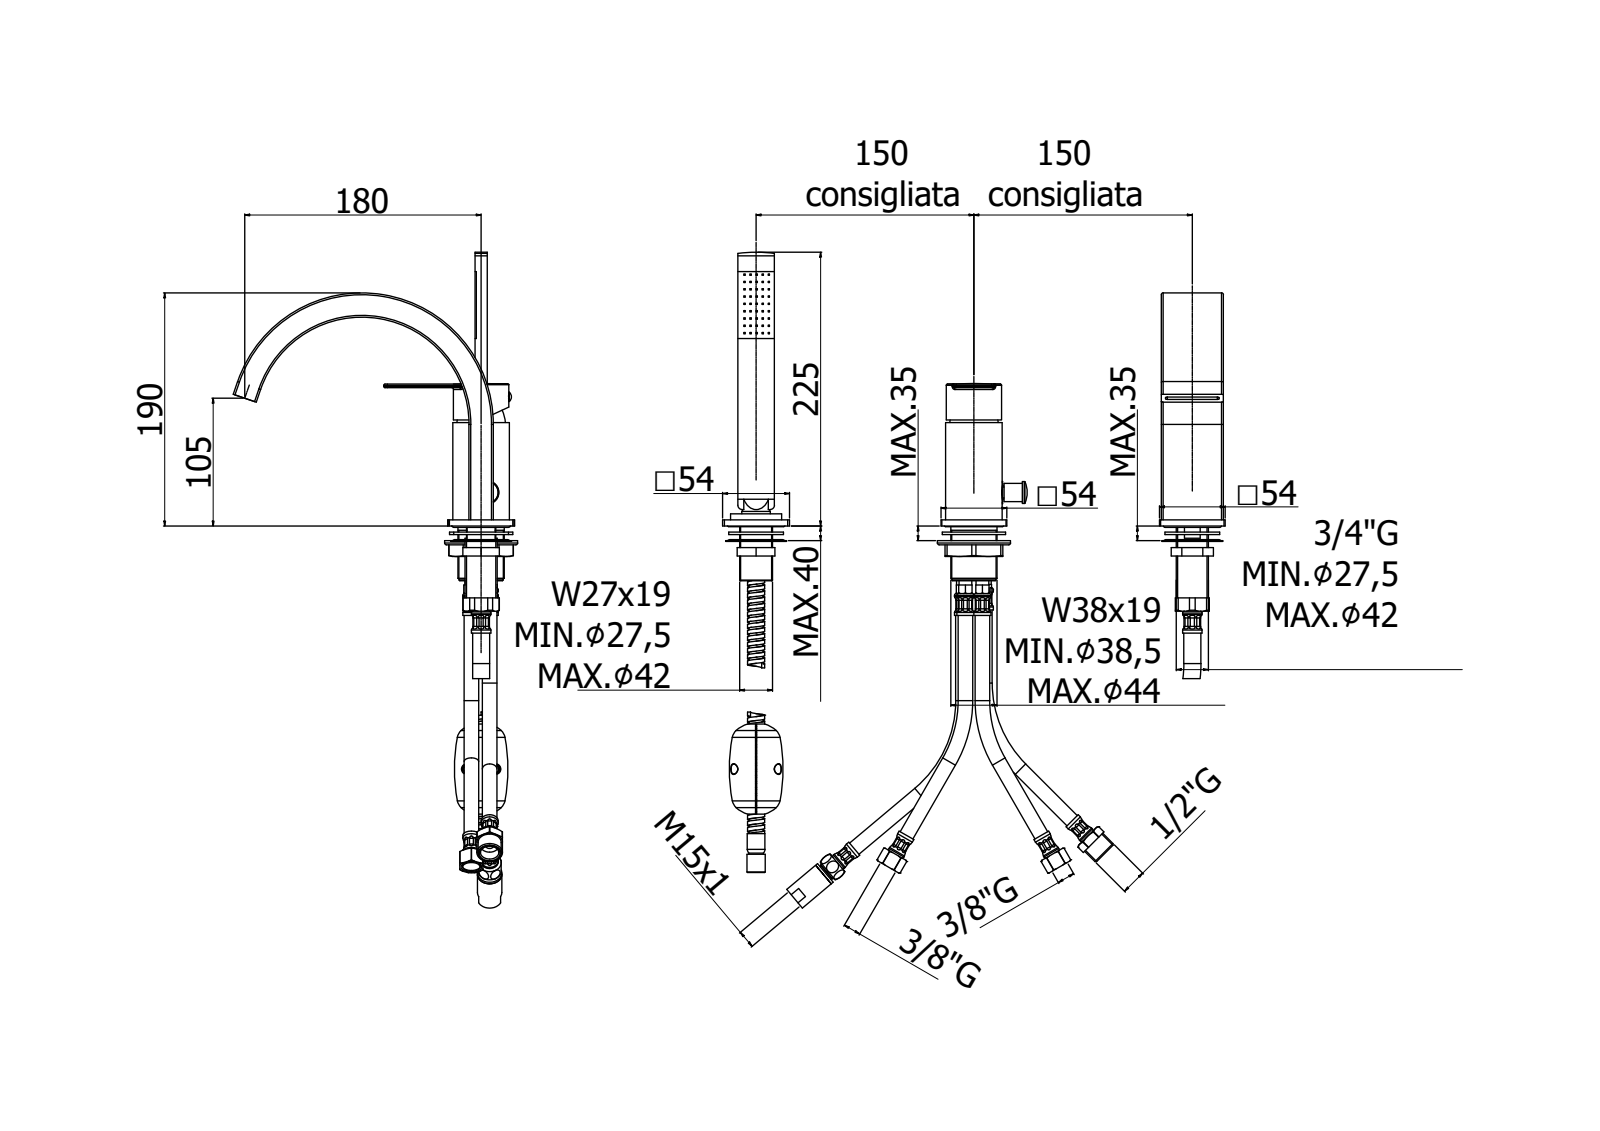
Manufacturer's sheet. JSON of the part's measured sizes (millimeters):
{"part_name": "TA040CR", "step_written_by": "CREO PARAMETRIC BY PTC INC, 2020044 (CONFIG_CONTROL_DESIGN)", "units": "millimeters", "bodies": {"solids": 5, "faces": 366, "planar": 119, "cylindrical": 141, "other": 106}, "overall_size": [356, 225, 216.96], "volume_mm3": 592233, "surface_area_mm2": 132571, "round_holes": [[7, 6], [5, 2], [2.5, 1], [3, 1], [3.4, 1], [3.5, 1], [4.2, 1], [6, 1], [7.2, 1], [9, 1], [9.5, 1], [13, 1]], "round_bosses_or_shafts": [[46.5, 1], [45.5, 1], [42.5, 1], [42, 1], [22.5, 1], [18.5, 1], [18, 1], [15, 1]], "partial_cylinders_radius": [[1.5, 20], [1, 6], [0.5, 2], [3, 2], [4, 2], [3.5, 1], [8.5, 1], [37.75, 1]], "face_to_face_distances": [5, 15, 51, 10, 20, 111.6, 259.5, 310.5, 30, 289.5], "hole_center_spacings": [3, 8.6, 10.63, 13.45, 14, 14.32, 15.13, 18.11]}
